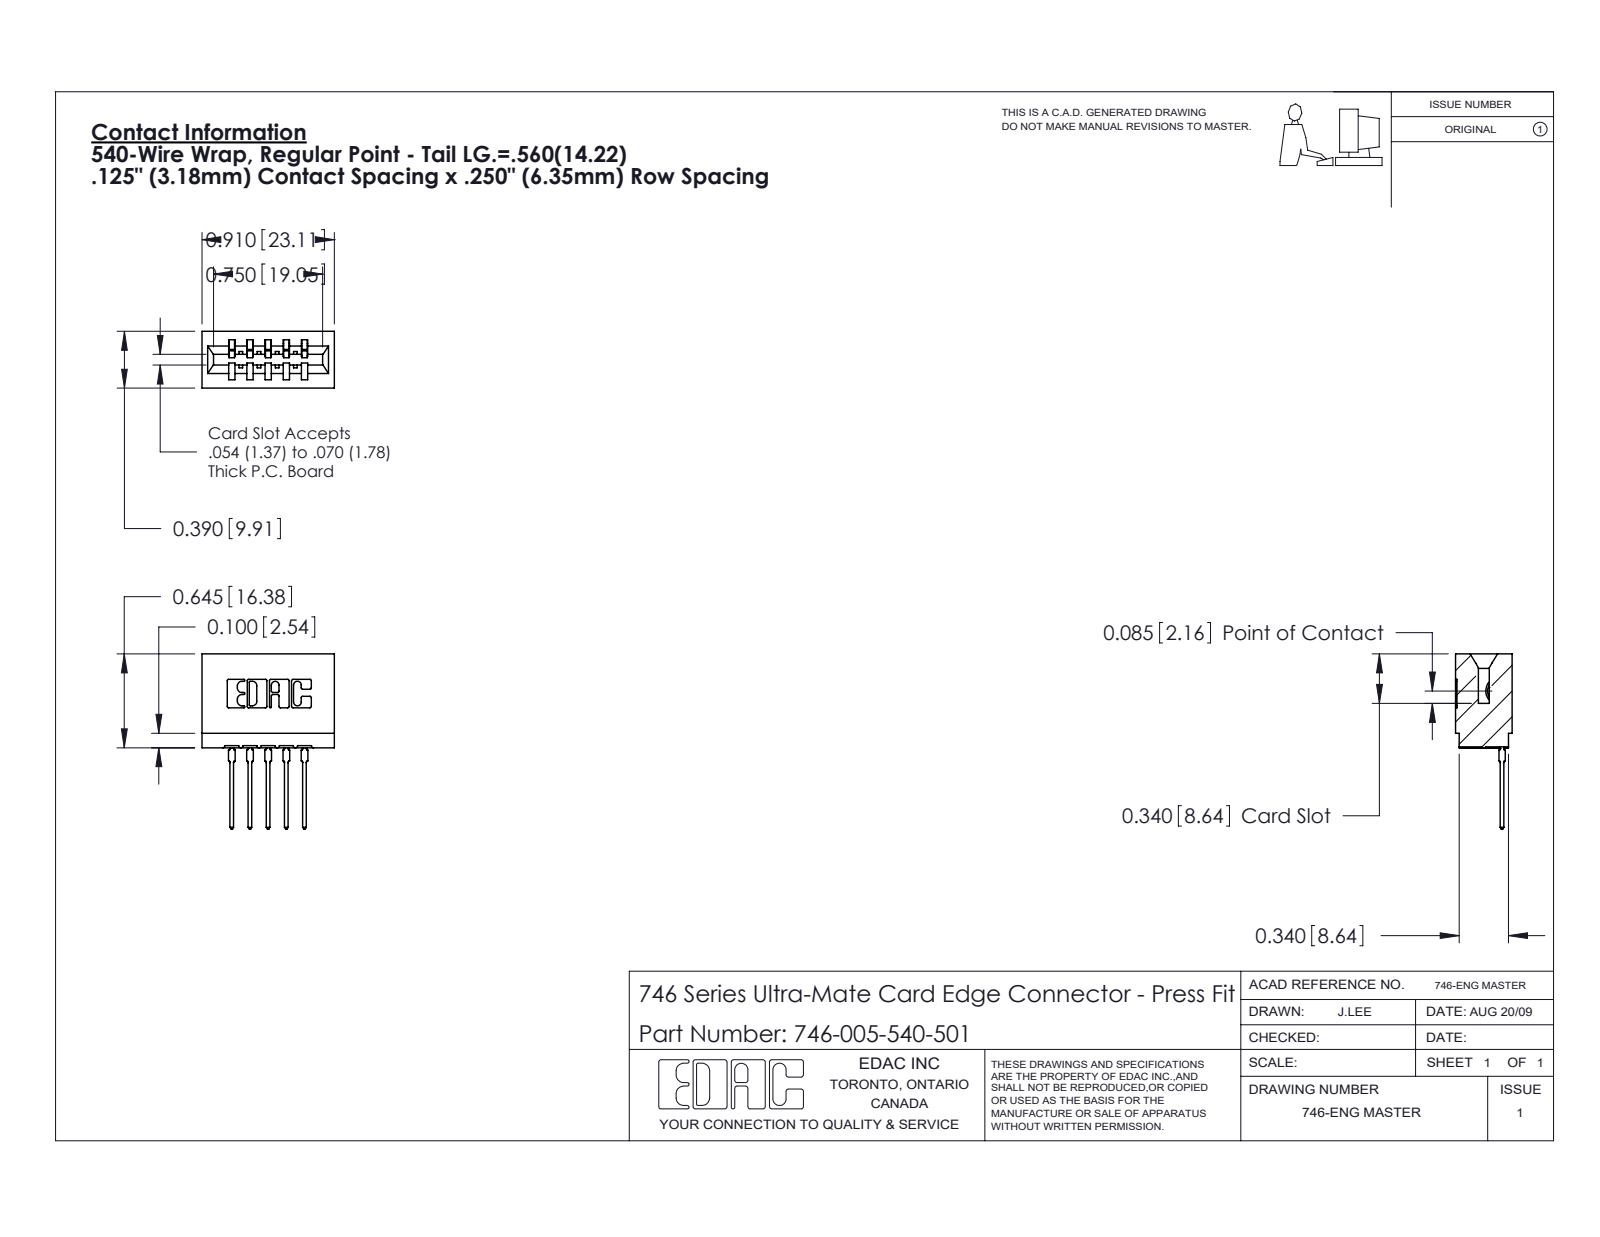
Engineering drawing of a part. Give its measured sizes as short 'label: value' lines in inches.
name: 746-005-540-501; 746-292-001_540; 746 Part_.340 Slot Depth - 01
written by: SolidWorks 2020 (CONFIG_CONTROL_DESIGN)
unit: in
bodies: 6 solids, 637 faces (370 planar, 137 cylindrical, 130 other)
size: 1.204 × 0.91 × 0.39
volume: 0.173 in³; area: 5.141 in²
rounds: 22× R0.01, 10× R0.021, 6× R0.007, 6× R0.015, 6× R0.031, 4× R0.005, 4× R0.011, 3× R0.026
face distances: 0.25, 0.042, 0.333, 0.125, 0.125, 0.057, 0.39, 0.083, 0.292, 0.208
